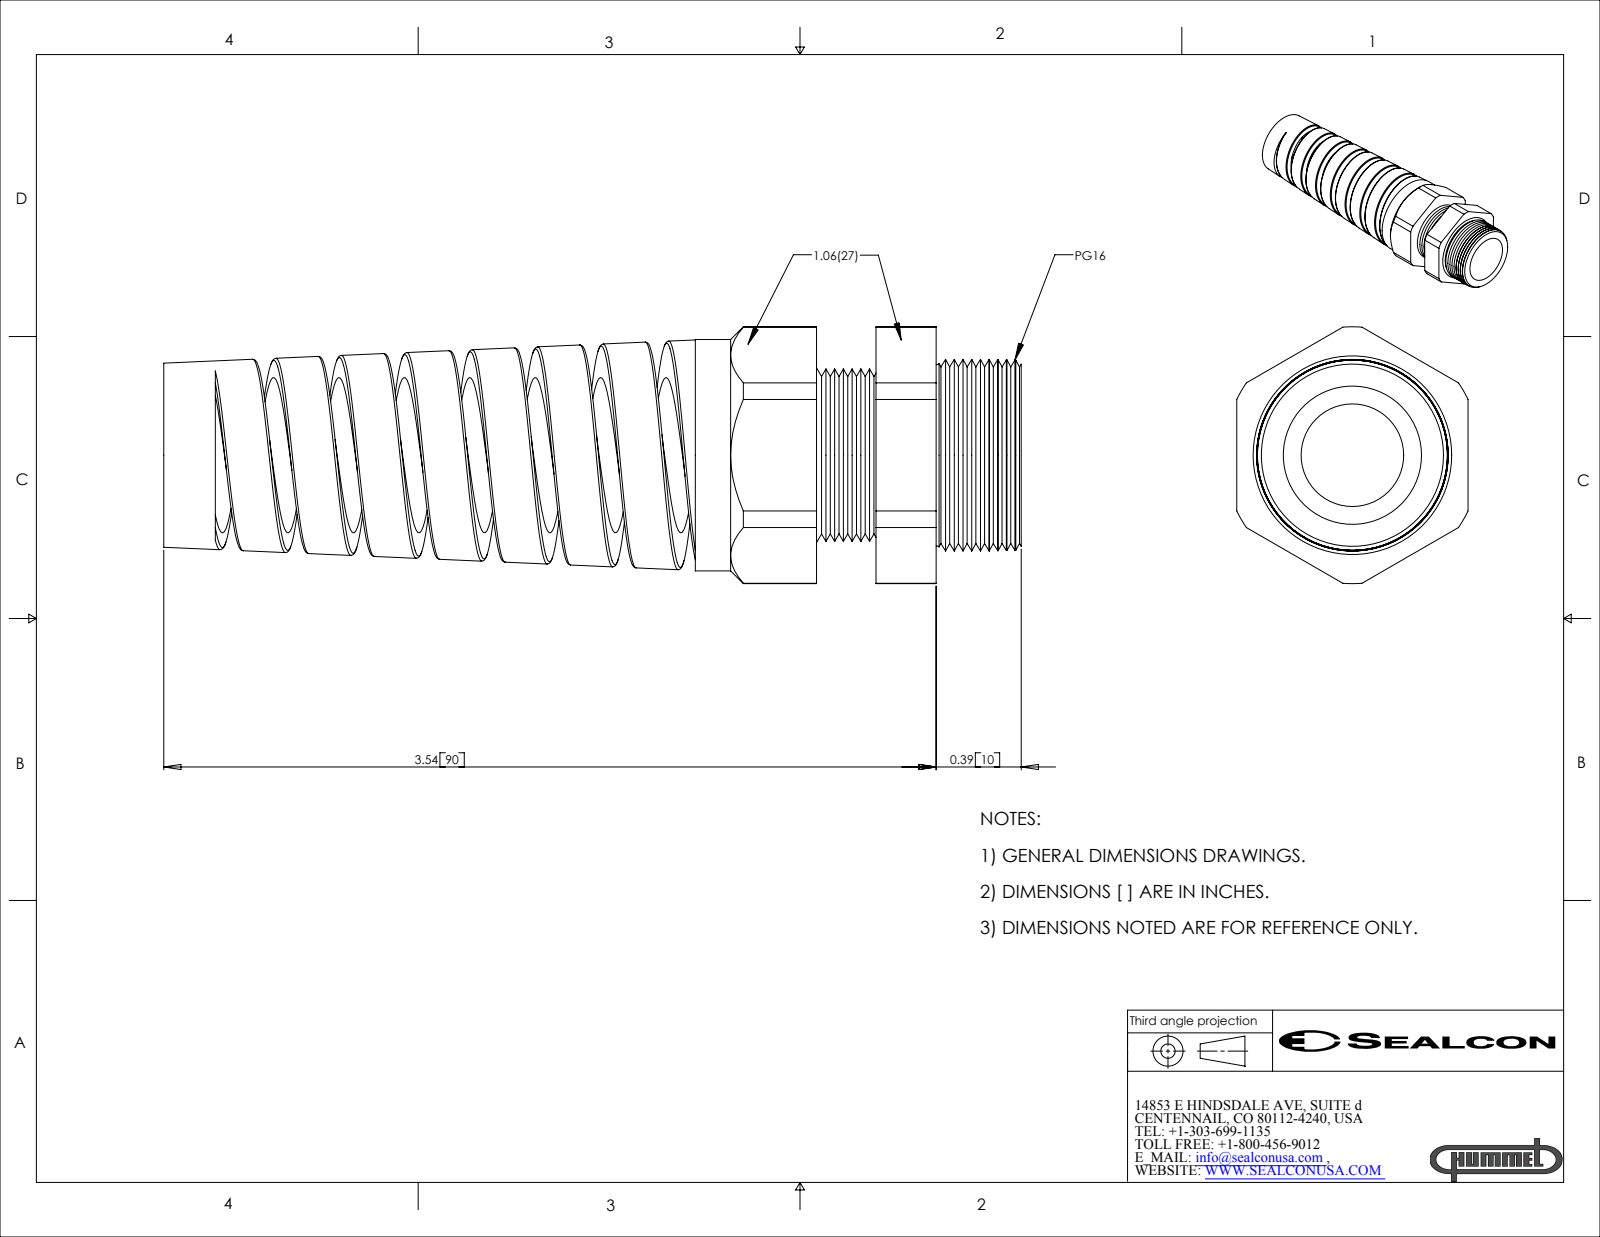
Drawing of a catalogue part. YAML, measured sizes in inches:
part_name: "CF16BA-GY"
step_written_by: "SolidWorks 2007 (CONFIG_CONTROL_DESIGN)"
units: inches
bodies: {solids: 2, faces: 176, planar: 24, cylindrical: 39, other: 113}
overall_size: [3.93, 1.177, 1.06]
volume: 1.358
surface_area: 27.72
round_holes:
  - {diameter: 0.47, count: 1}
  - {diameter: 0.712, count: 1}
  - {diameter: 0.801, count: 1}
round_bosses_or_shafts:
  - {diameter: 1.06, count: 1}
partial_cylinders:
  - {radius: 0.366, count: 1}
  - {radius: 0.588, count: 1}
face_to_face_distances: [1.06, 0.273, 0.548, 0.276, 0.938, 0.665, 0.39, 0.482, 0.755, 1.03]
